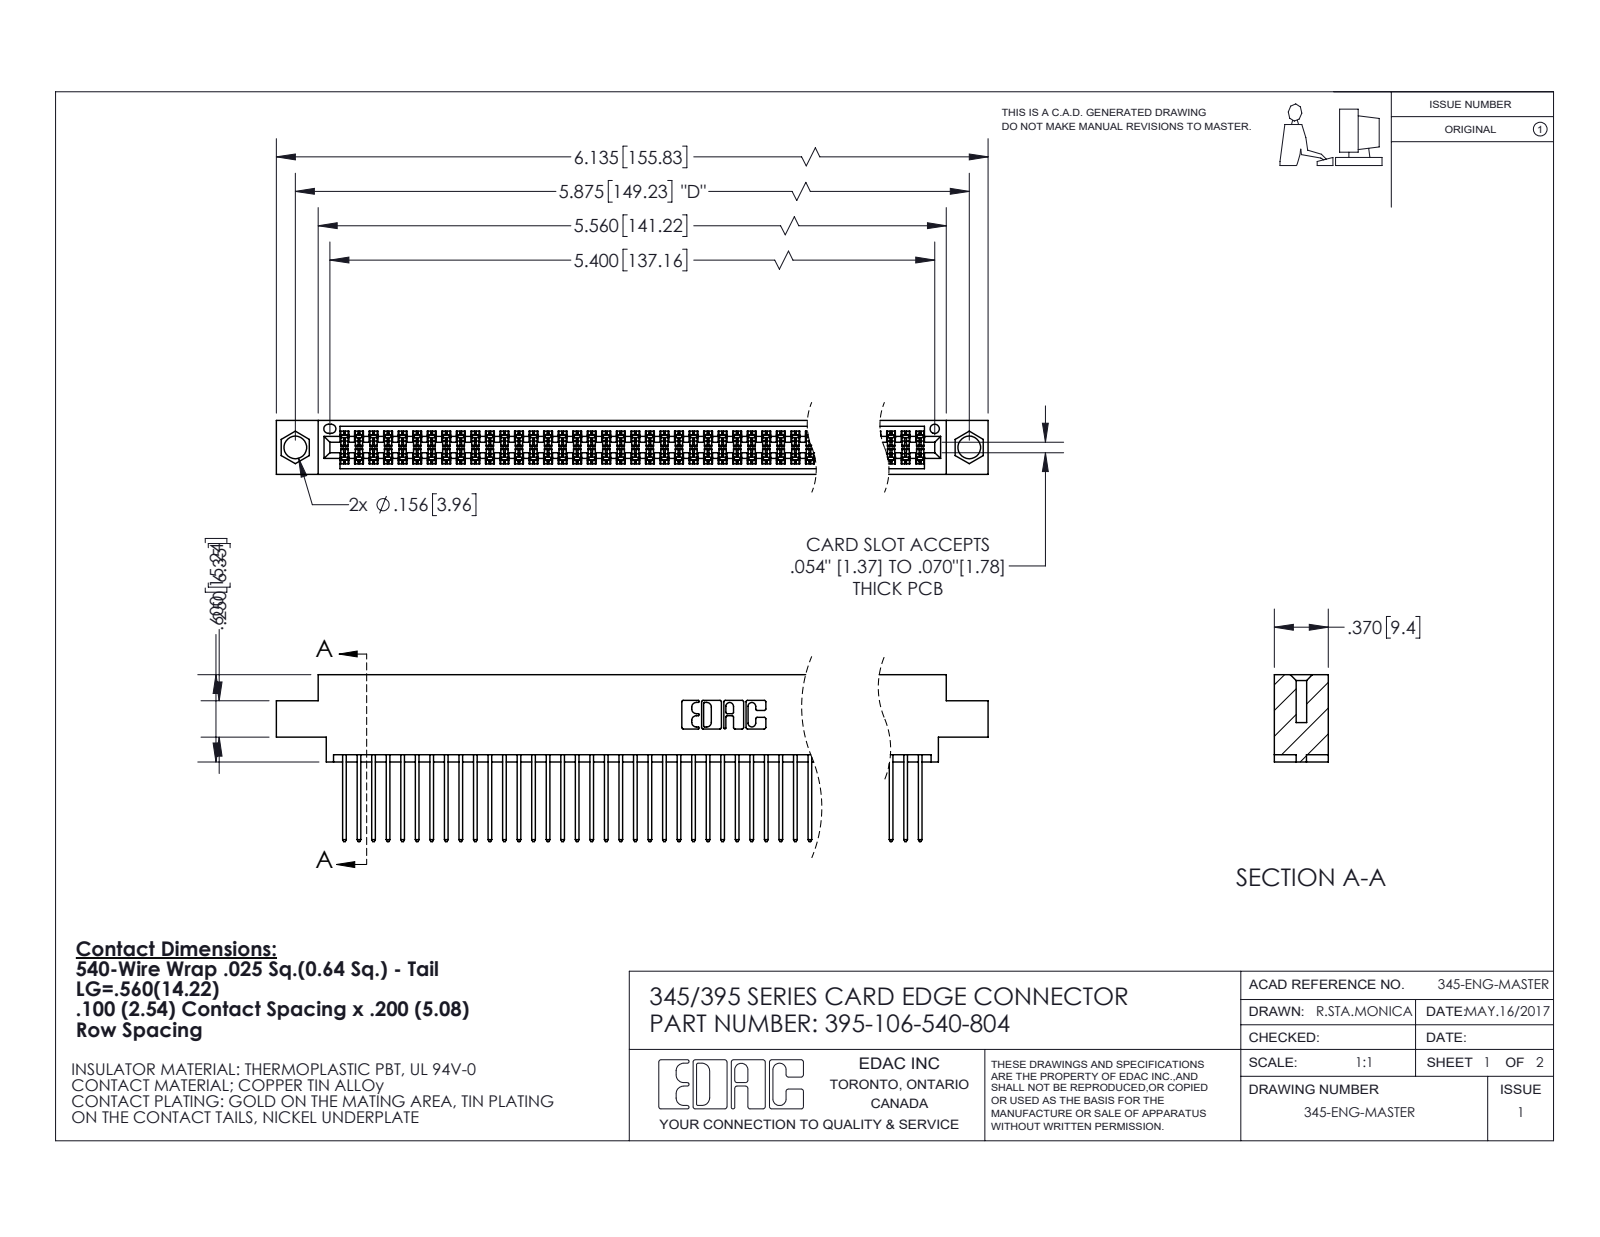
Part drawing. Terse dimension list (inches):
name: 345-292-001_345-293-140; 345 Part_0.170 Offset - 0.156 Dia-TI; 395-106-540-804
written by: SolidWorks 2020 (CONFIG_CONTROL_DESIGN)
unit: in
bodies: 107 solids, 5444 faces (3596 planar, 1848 cylindrical, 0 other)
size: 6.135 × 1.147 × 0.37
volume: 0.941 in³; area: 38.55 in²
holes: 2× ⌀0.156, 1× ⌀0.064
rounds: 212× R0.006, 106× R0.01, 22× R0.01, 6× R0.007, 6× R0.031, 3× R0.026, 2× R0.014, 2× R0.019
face distances: 0.072, 0.298, 0.2, 0.098, 0.272, 0.025, 0.37, 0.225, 0.175, 0.149
hole spacings: 0.27, 5.639, 5.875
